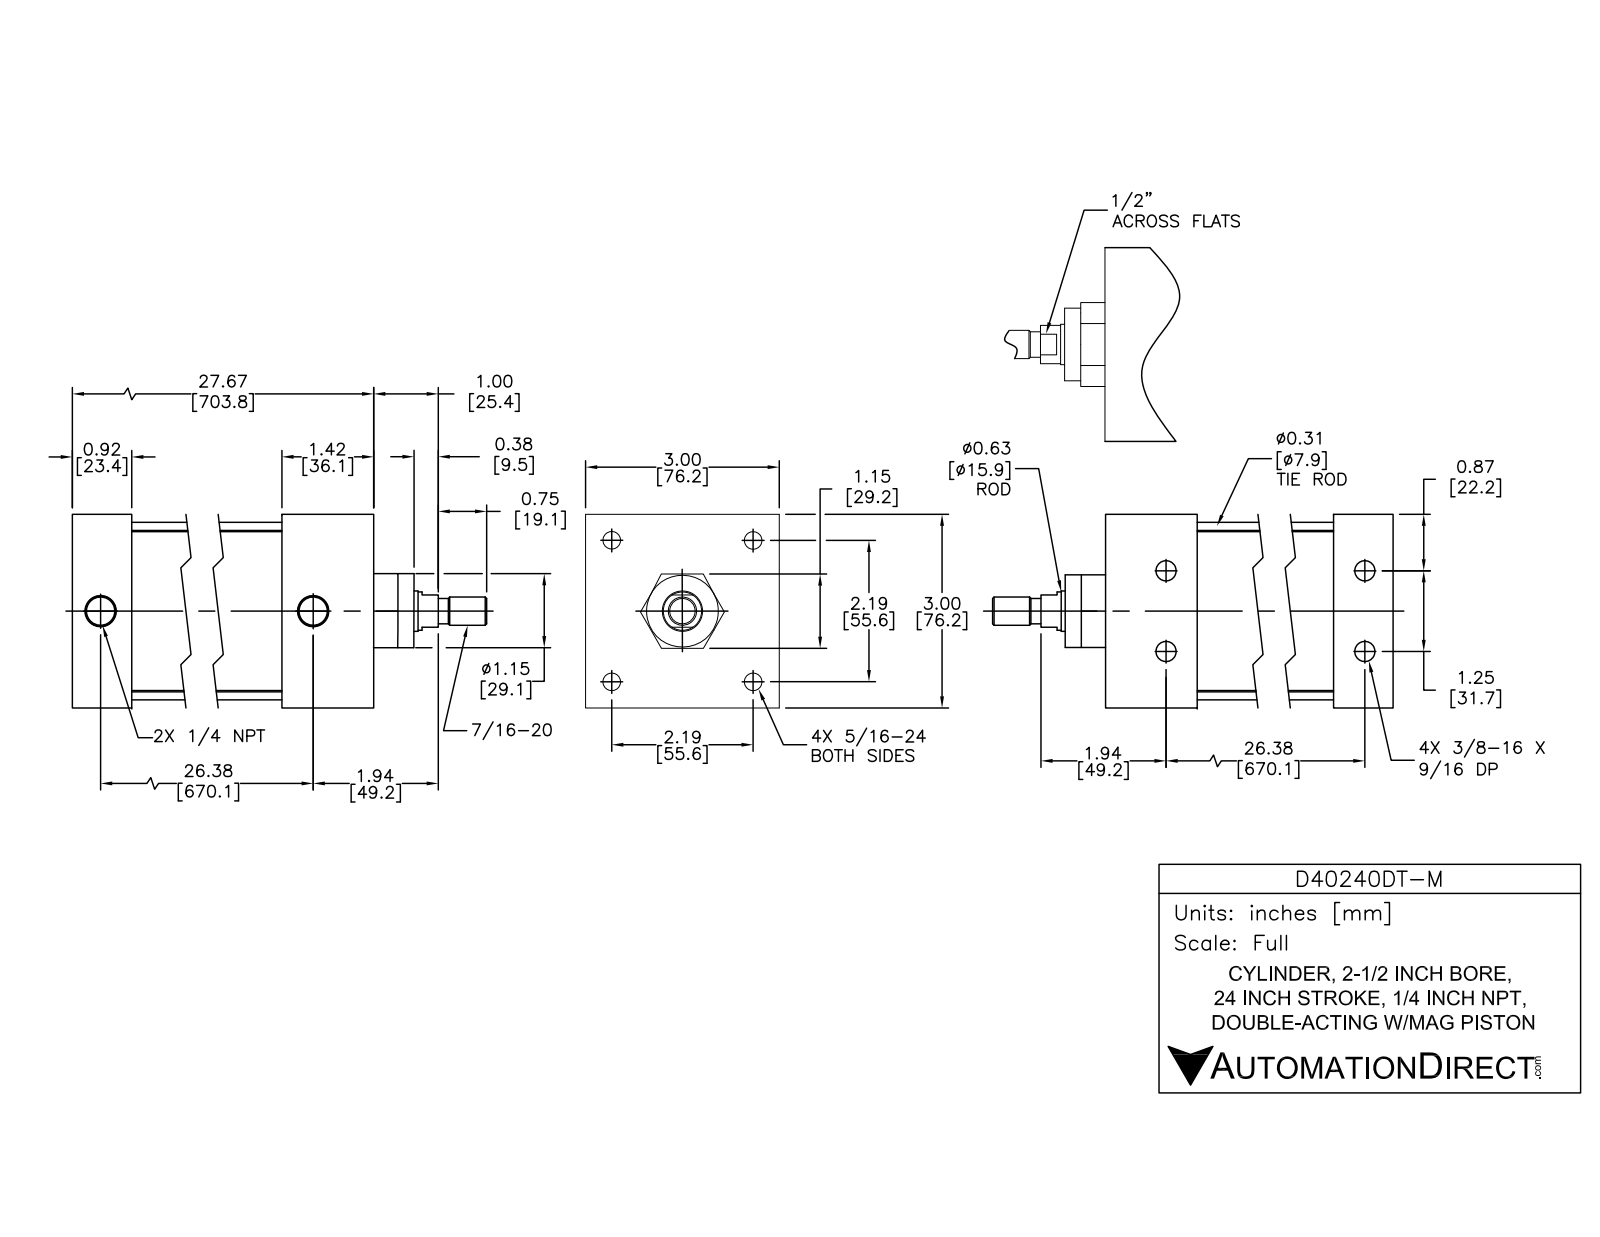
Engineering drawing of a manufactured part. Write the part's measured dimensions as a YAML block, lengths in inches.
part_name: "D40240DT-M BODY; D40240DT-M; D40240DT-M PISTON"
step_written_by: "SolidWorks 2015 (AUTOMOTIVE_DESIGN)"
units: inches
bodies: {solids: 12, faces: 298, planar: 94, cylindrical: 114, other: 90}
overall_size: [29.496, 3, 3]
volume: 67.24
surface_area: 680.5
round_holes:
  - {diameter: 0.267, count: 4}
  - {diameter: 0.307, count: 4}
  - {diameter: 0.359, count: 4}
  - {diameter: 0.5, count: 4}
  - {diameter: 0.297, count: 2}
  - {diameter: 0.477, count: 2}
  - {diameter: 0.625, count: 1}
  - {diameter: 0.628, count: 1}
  - {diameter: 2.5, count: 1}
round_bosses_or_shafts:
  - {diameter: 0.484, count: 4}
  - {diameter: 0.313, count: 4}
  - {diameter: 0.282, count: 4}
  - {diameter: 2.75, count: 1}
  - {diameter: 2.497, count: 1}
  - {diameter: 1.12, count: 1}
  - {diameter: 0.622, count: 1}
  - {diameter: 0.59, count: 1}
partial_cylinders:
  - {radius: 0.3, count: 4}
face_to_face_distances: [3, 27.746, 26.726, 1.02, 1.42, 25.306, 26.326, 1, 26.826, 25.406]
hole_center_spacings: [1.556, 2.2, 26.378, 26.37, 0.625, 0.625, 1.25, 3.111]
